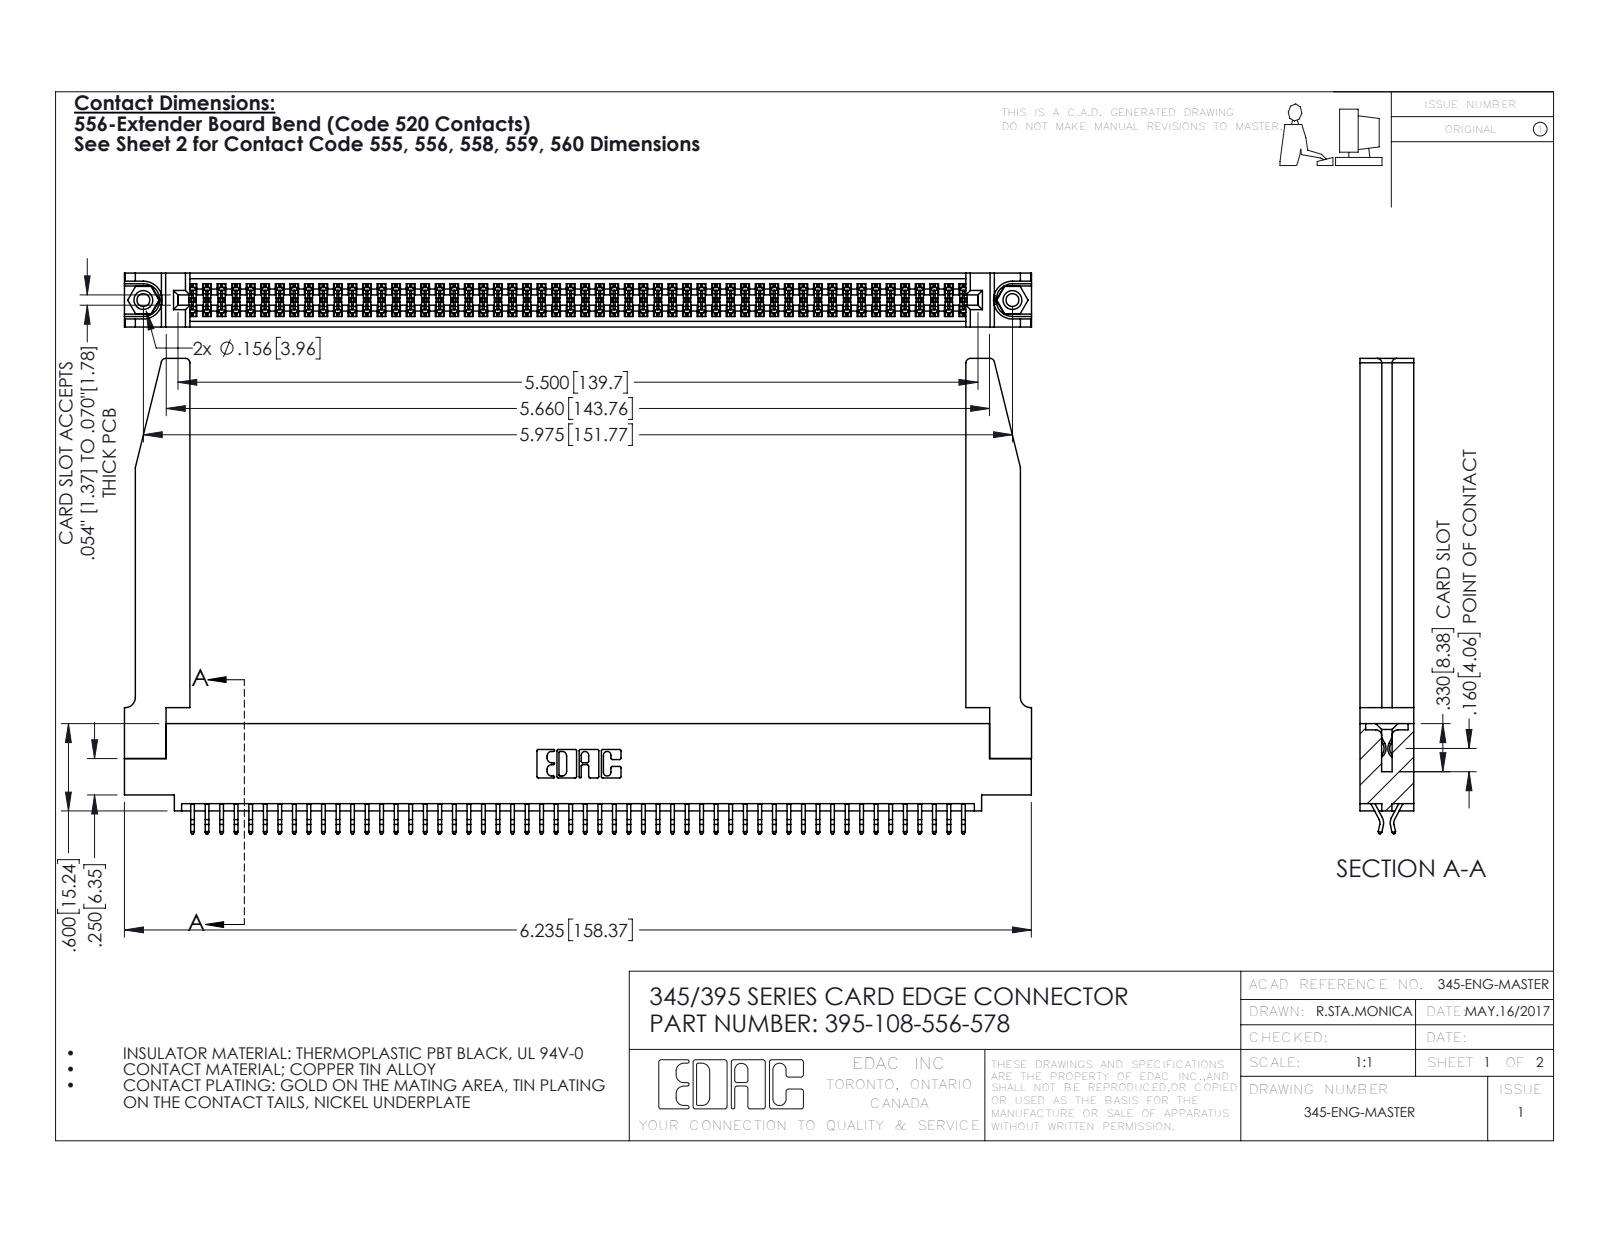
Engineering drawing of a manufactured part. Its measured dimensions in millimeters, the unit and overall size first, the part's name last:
Units: millimetres
Overall size (bounding box): 158.4 × 83 × 9.4
Round holes (diameter × count): ⌀2.3 ×2, ⌀3.2 ×2, ⌀4 ×2, ⌀1.6 ×1
Round bosses / shafts (diameter × count): ⌀3.9 ×2
Partial cylindrical surfaces — rounded edges, fillets, slot ends (radius × count): R0.2 ×162, R0.3 ×22, R0.8 ×8, R0.2 ×6, R0.8 ×6, R0.7 ×3, R0.3 ×2, R0.4 ×2
Main face-to-face distances: 1.8, 9.4, 7.6, 0.6, 5.1, 2.5, 6.9, 5.7, 4.4, 3.8
Hole centre spacings: 6.9, 145.8, 151.8
Volume: 23 190 mm³ · Surface area: 29 860 mm²
Bodies: 113 solids, 6412 faces (4222 planar, 2138 cylindrical, 52 other)
Part name (STEP PRODUCT): 345-220-078_345-220-078; 345-292-001_556 Tail; 345-250-001_345-250-001-102; 345 Part_0.110 Offset - 0.156 Dia-TH (+1 more)
STEP written by: SolidWorks 2016 (CONFIG_CONTROL_DESIGN)
